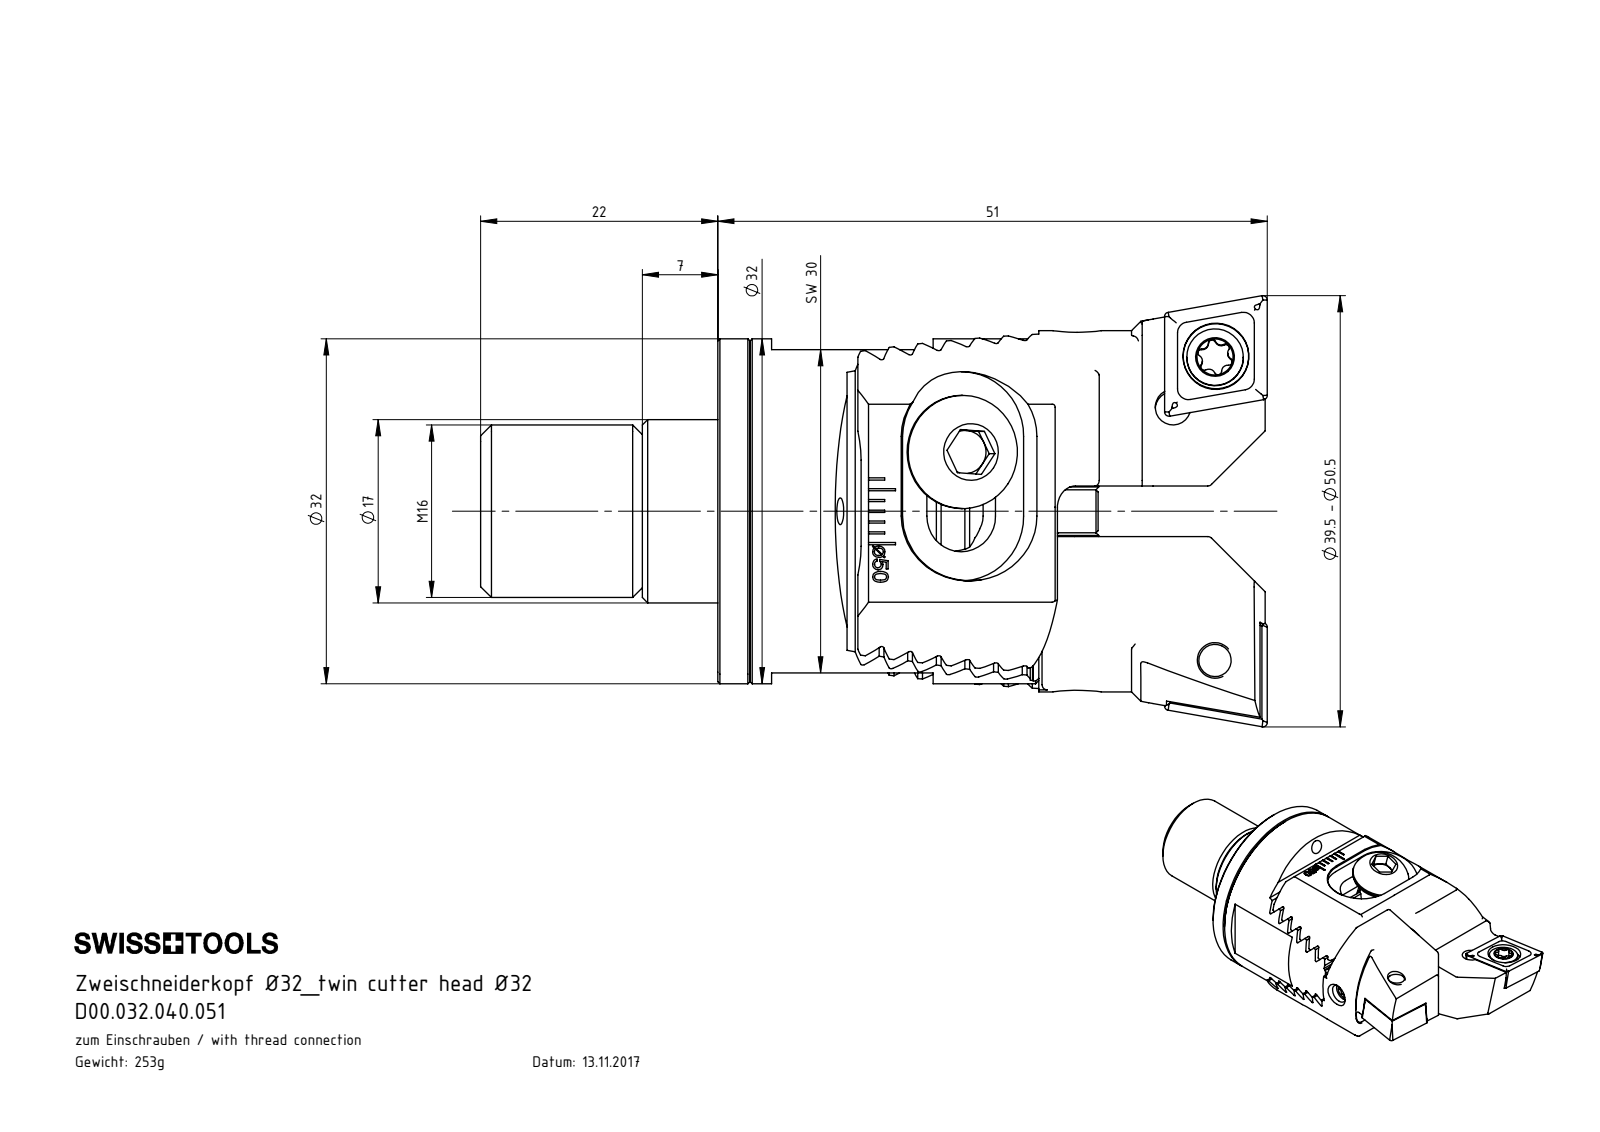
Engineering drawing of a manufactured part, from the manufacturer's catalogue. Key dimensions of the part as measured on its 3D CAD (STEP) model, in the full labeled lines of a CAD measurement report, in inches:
Part name (STEP PRODUCT): HP5-Z32.040.051_A; Z32-xxx.001.021_B; Z20-ER2.001.013_A; D00.032.040.051 (+8 more)
STEP written by: SolidWorks 2017 (CONFIG_CONTROL_DESIGN)
Units: inches
Bodies: 16 solids, 985 faces (457 planar, 232 cylindrical, 296 other)
Overall size (bounding box): 2.874 × 1.575 × 1.26
Volume: 1.965 in³ · Surface area: 30.38 in²
Round holes (diameter × count): ⌀0.098 ×5, ⌀0.13 ×5, ⌀0.063 ×2, ⌀0.079 ×2, ⌀0.173 ×2, ⌀0.197 ×2, ⌀0.24 ×2, ⌀0.252 ×2, ⌀0.268 ×2, ⌀0.138 ×1, ⌀0.402 ×1, ⌀0.492 ×1
Round bosses / shafts (diameter × count): ⌀0.157 ×4, ⌀0.413 ×2, ⌀0.402 ×2, ⌀0.236 ×2, ⌀0.207 ×2, ⌀1.26 ×1, ⌀0.63 ×1, ⌀0.472 ×1
Partial cylindrical surfaces — rounded edges, fillets, slot ends (radius × count): R0.02 ×16, R0.008 ×14, R0.008 ×12, R0.013 ×12, R0.023 ×12, R0.079 ×4, R0.13 ×4, R0.236 ×4
Main face-to-face distances: 0.094, 0.187, 0.281, 0.118, 0.375, 0.375, 0.193, 0.469, 0.281, 0.096
Hole centre spacings: 0.239, 0.244, 0.954, 0.958, 1.128, 0.354, 0.355, 0.685
